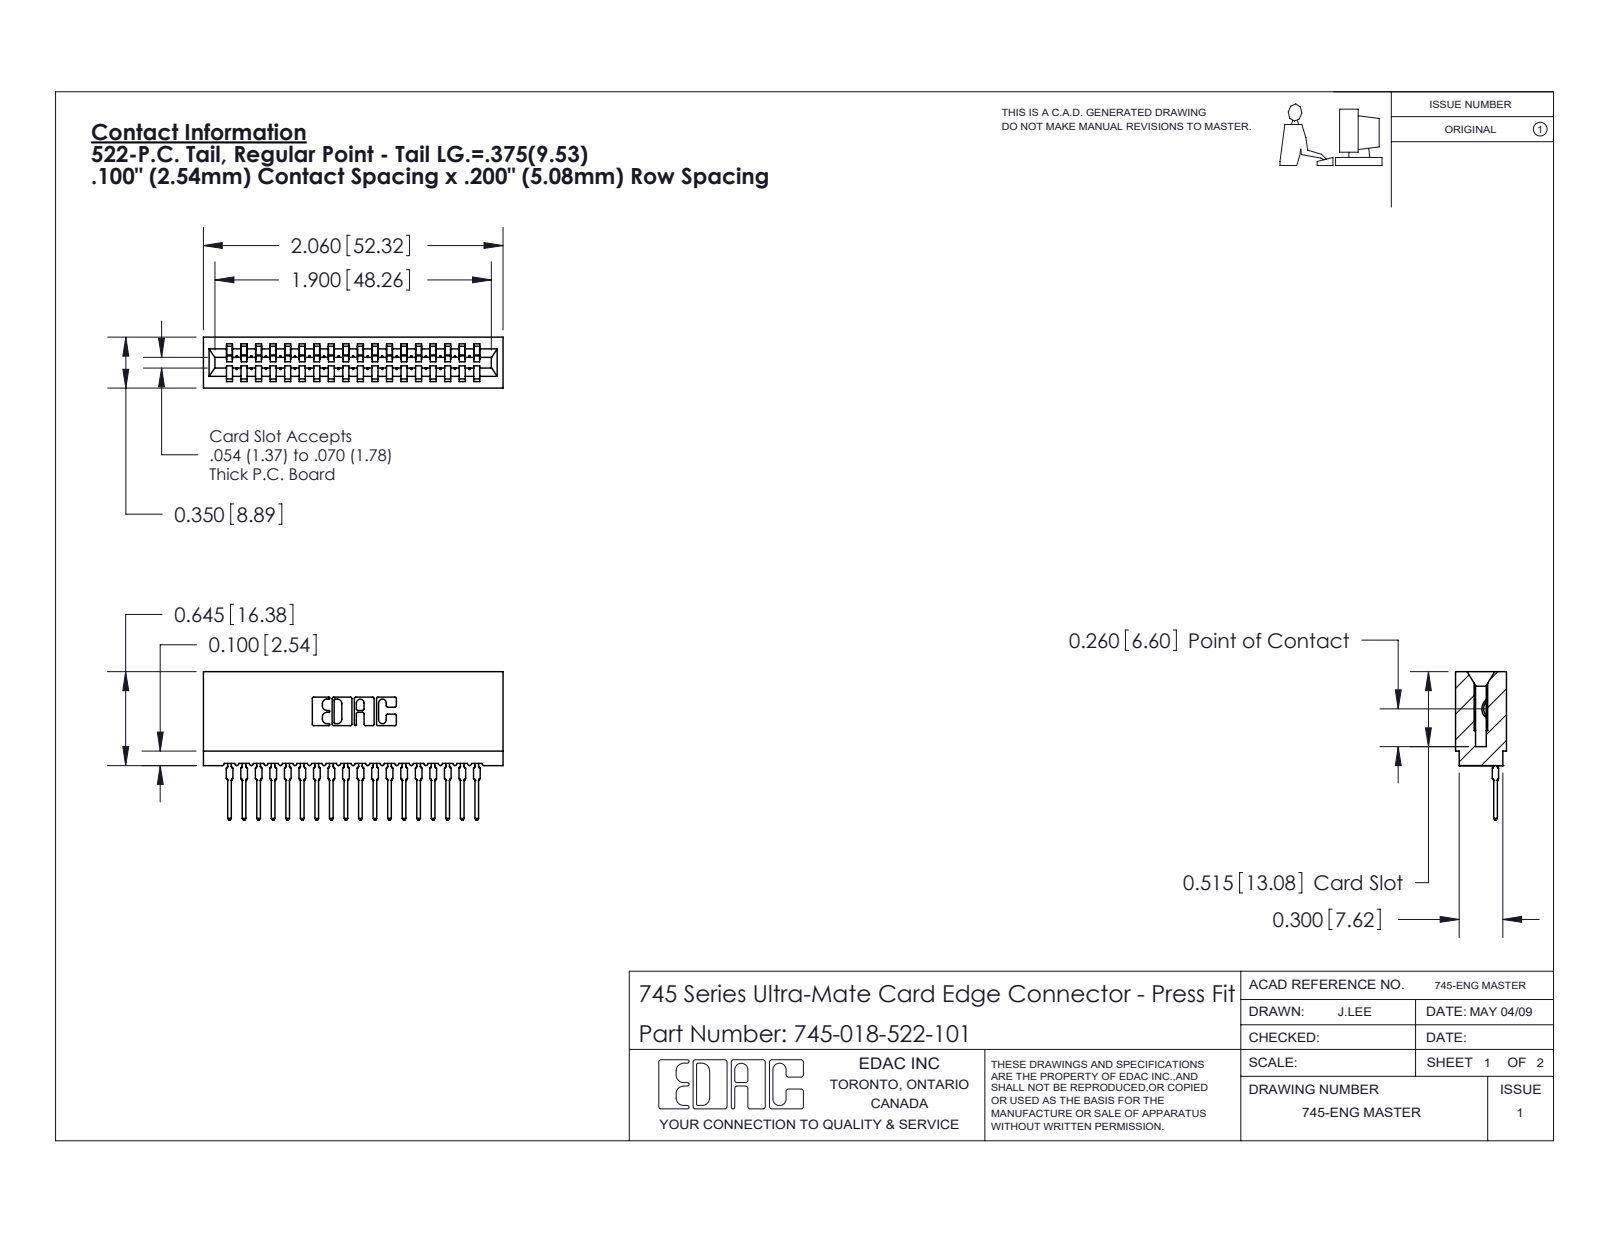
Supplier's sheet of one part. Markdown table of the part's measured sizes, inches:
| quantity | value |
| --- | --- |
| part name | 745-292-001_522; 745 Part_Insulator Option - 01; 745-018-522-101 |
| STEP written by | SolidWorks 2020 (CONFIG_CONTROL_DESIGN) |
| units | inches |
| bodies | 19 solids, 2111 faces (1261 planar, 382 cylindrical, 468 other) |
| overall size | 2.06 × 1.021 × 0.35 |
| volume | 0.287 in³ |
| surface area | 12.91 in² |
| partial cylindrical surfaces (radius × count) | 0.015 × 36, 0.021 × 36, 0.01 × 22, 0.007 × 6, 0.031 × 6, 0.005 × 4, 0.011 × 4, 0.026 × 3 |
| main face-to-face distances | 0.1, 0.2, 0.3, 0.4, 0.5, 0.35, 0.6, 0.7, 0.138, 0.212 |
